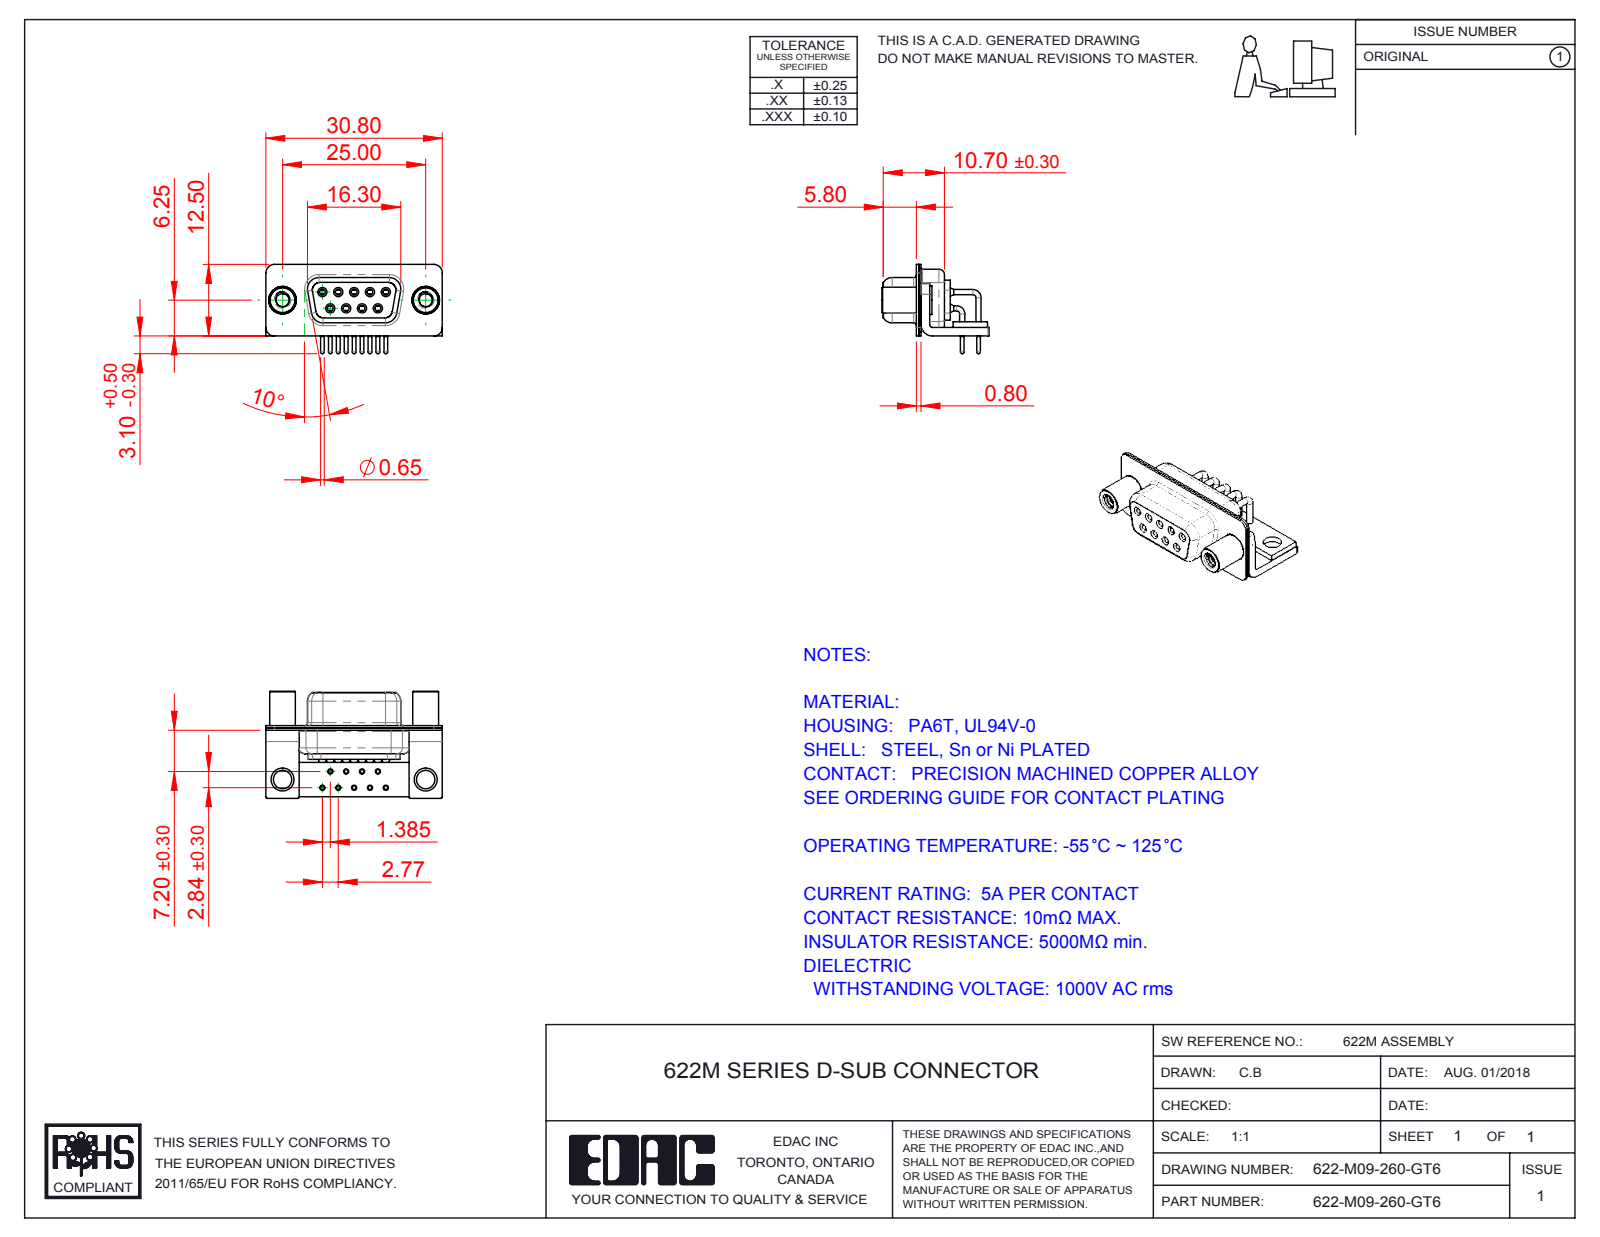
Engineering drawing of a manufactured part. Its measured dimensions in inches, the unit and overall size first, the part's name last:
Units: inches
Overall size (bounding box): 1.213 × 0.736 × 0.614
Round holes (diameter × count): ⌀0.035 ×9, ⌀0.039 ×9, ⌀0.043 ×9, ⌀0.067 ×9, ⌀0.071 ×9, ⌀0.079 ×9, ⌀0.089 ×2, ⌀0.126 ×2, ⌀0.157 ×2, ⌀0.189 ×2
Round bosses / shafts (diameter × count): ⌀0.063 ×9, ⌀0.059 ×9, ⌀0.035 ×9, ⌀0.026 ×9, ⌀0.197 ×2, ⌀0.193 ×2, ⌀0.177 ×2
Partial cylindrical surfaces — rounded edges, fillets, slot ends (radius × count): R0.01 ×16, R0.059 ×16, R0.079 ×13, R0.053 ×8, R0.063 ×8, R0.02 ×5, R0.024 ×4, R0.026 ×4
Main face-to-face distances: 0.016, 0.031, 0.091, 0.075, 0.059, 0.039, 0.368, 0.057, 0.335, 0.352
Hole centre spacings: 0.124, 0.109, 0.218, 0.198, 0.198, 0.327, 0.294, 0.295
Volume: 0.138 in³ · Surface area: 9.054 in²
Bodies: 17 solids, 874 faces (230 planar, 426 cylindrical, 218 other)
Part name (STEP PRODUCT): 622M Shell Front_09 Contacts; 622M Housing_09 Contacts; 622-M09-260-GT6; 622M Stabilizer Board_09 Contacts (+5 more)
STEP written by: SolidWorks 2016 (CONFIG_CONTROL_DESIGN)
